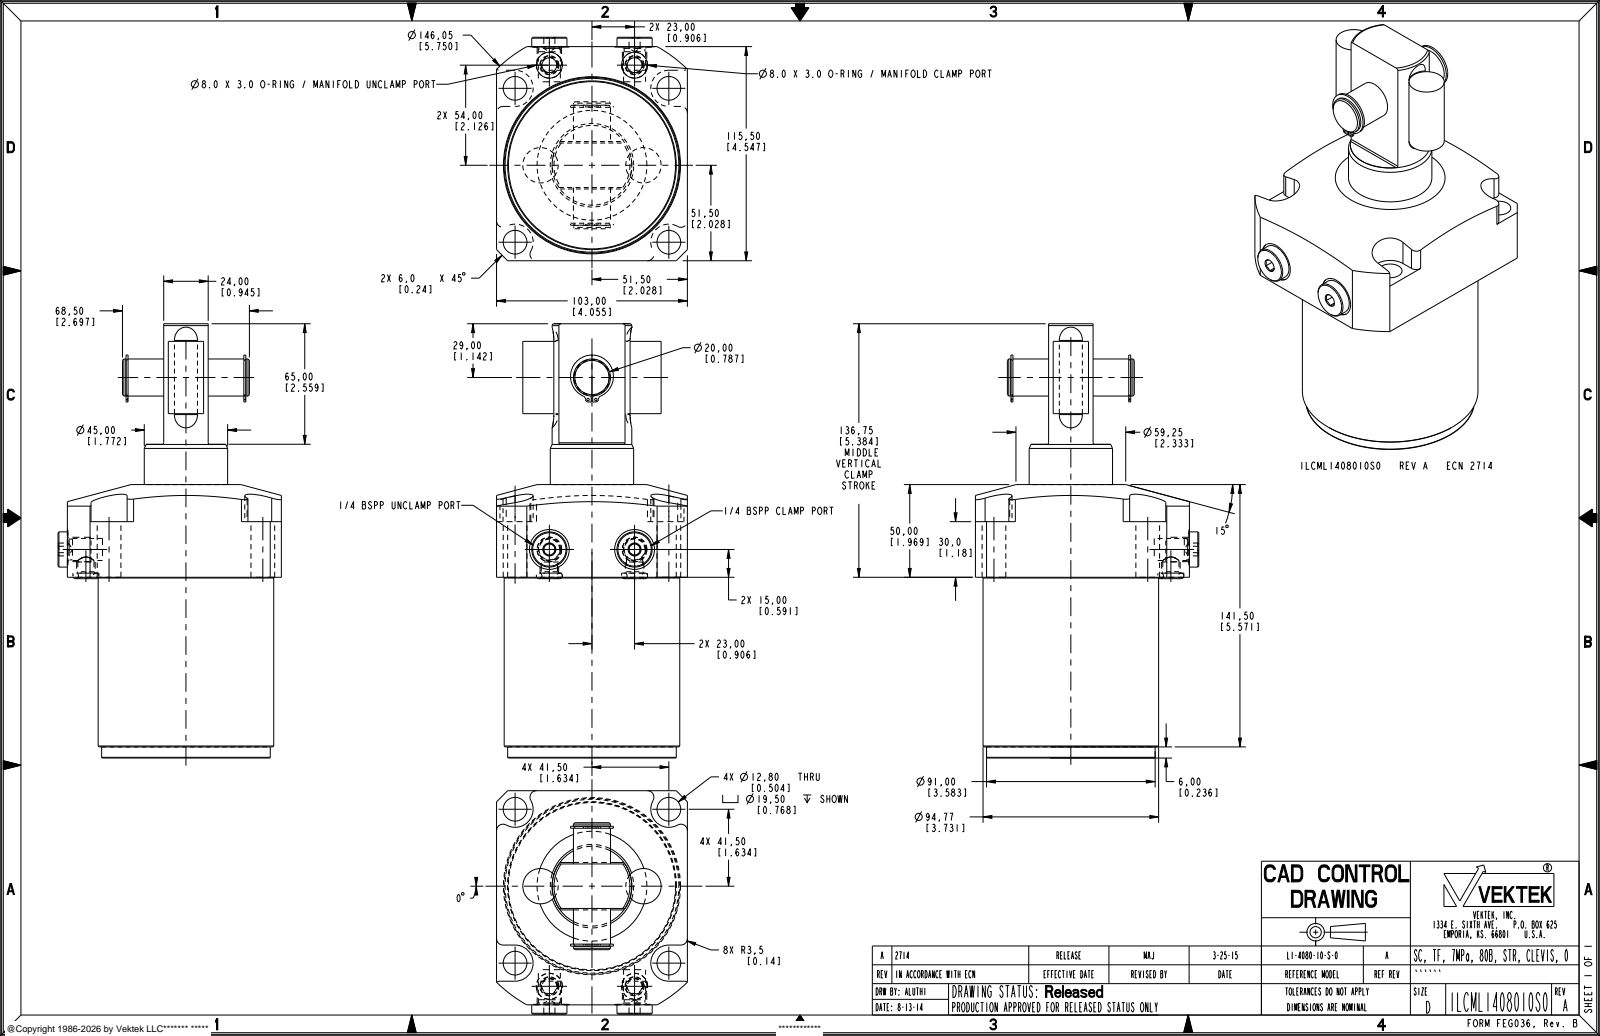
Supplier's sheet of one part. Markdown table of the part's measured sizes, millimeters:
| quantity | value |
| --- | --- |
| part name | ILCML1408010S0 |
| STEP written by | PRO/ENGINEER BY PARAMETRIC TECHNOLOGY CORPORATION, 2013320 (AUTOMOTIVE_DESIGN) |
| units | millimeters |
| bodies | 3 solids, 239 faces (85 planar, 106 cylindrical, 48 other) |
| overall size | 234.25 × 120.55 × 103 |
| volume | 1 321 000 mm³ |
| surface area | 98 235 mm² |
| round holes (diameter × count) | 12.8 × 4, 1.32 × 2, 6 × 2, 8.75 × 2, 11.89 × 2, 14 × 2, 21.5 × 2, 19.5 × 1 |
| round bosses / shafts (diameter × count) | 19 × 2, 13.16 × 2, 11.2 × 2, 10 × 2, 94.77 × 1, 91 × 1, 45 × 1, 43 × 1 |
| partial cylindrical surfaces (radius × count) | 3.5 × 8, 9.53 × 4, 9.75 × 4, 0.8 × 2, 1.32 × 2, 1.99 × 2, 73.03 × 1 |
| main face-to-face distances | 103, 97.5, 115.5, 63.5, 52, 39.5, 76, 24, 147.5, 50 |
| hole center spacings | 83, 12.06, 22.33, 46, 65.7, 83.53, 84.69, 95.56 |
